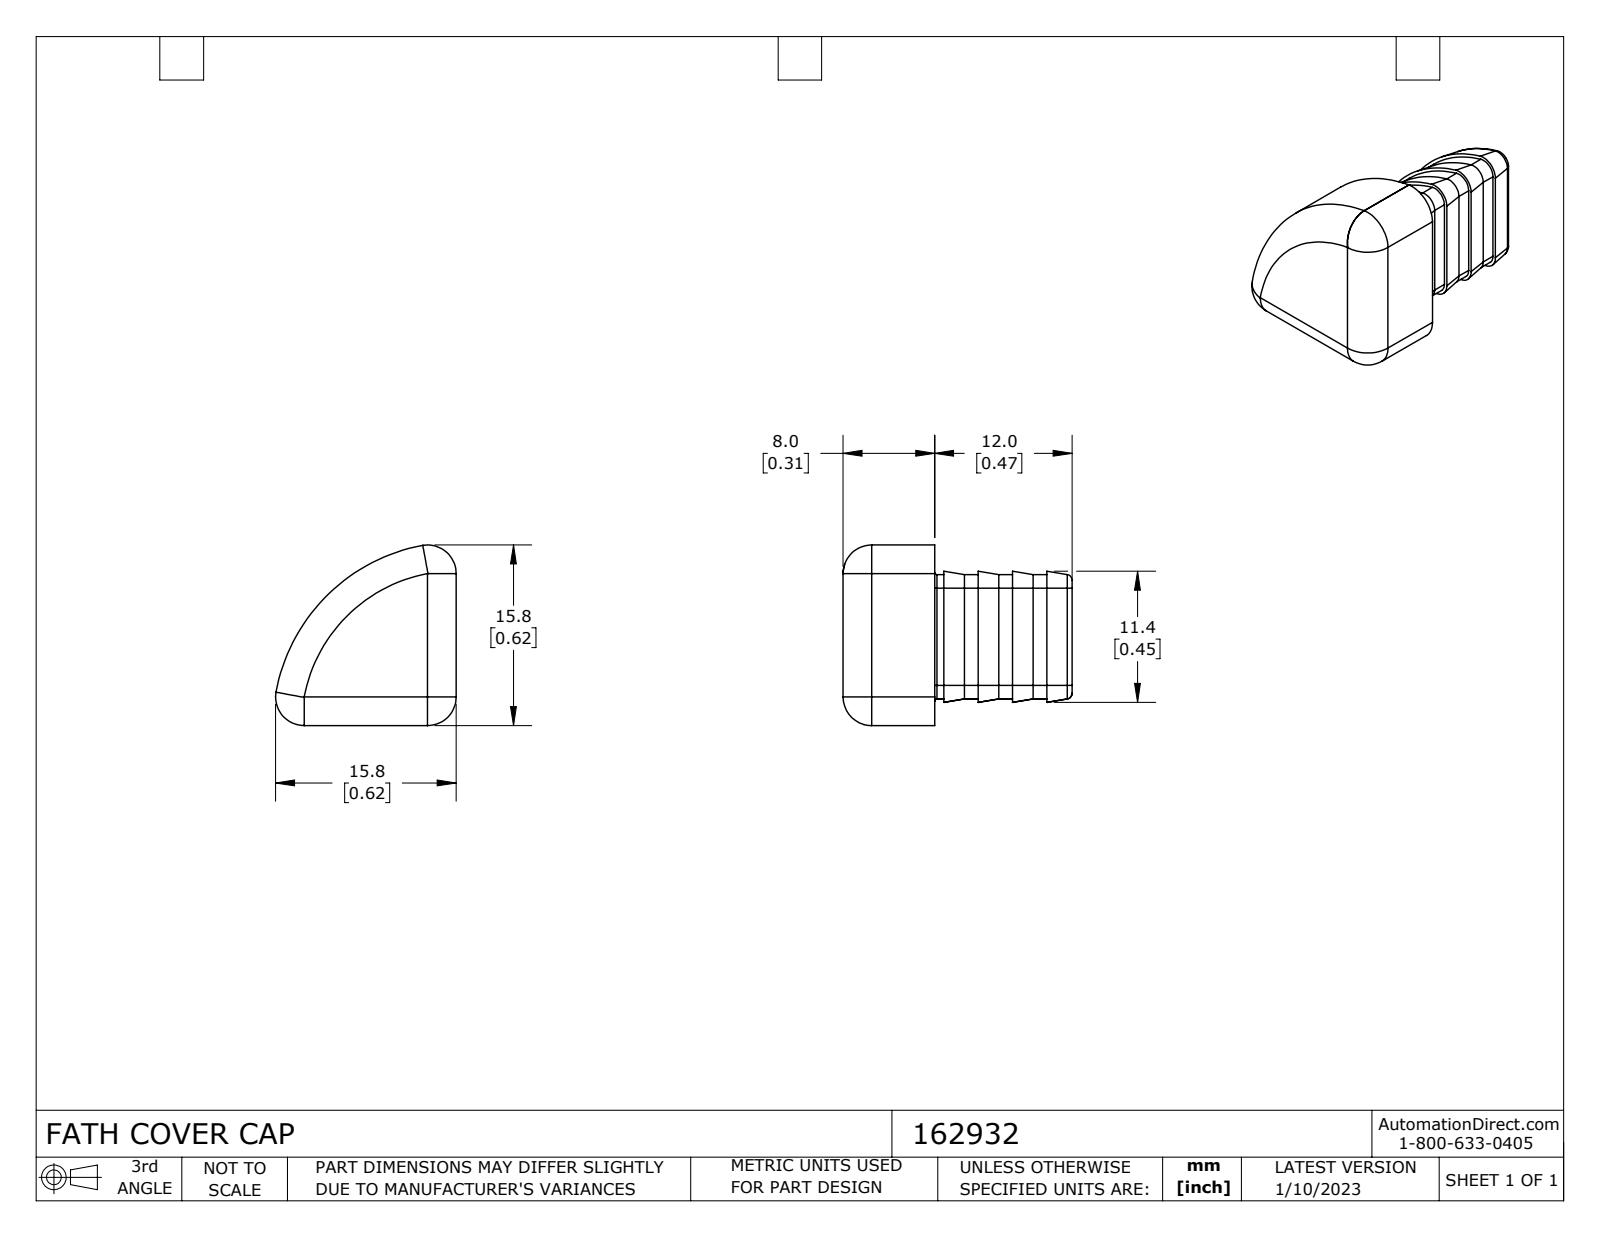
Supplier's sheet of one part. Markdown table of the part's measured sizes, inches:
| quantity | value |
| --- | --- |
| part name | 162932 |
| STEP written by | SolidWorks 2021 (CONFIG_CONTROL_DESIGN) |
| units | inches |
| bodies | 1 solid, 93 faces (30 planar, 31 cylindrical, 32 other) |
| overall size | 0.787 × 0.62 × 0.62 |
| volume | 0.148 in³ |
| surface area | 2.194 in² |
| round holes (diameter × count) | 0.118 × 2 |
| partial cylindrical surfaces (radius × count) | 0.098 × 5, 0.046 × 3, 0.008 × 2, 0.02 × 2, 0.538 × 1, 0.63 × 1 |
| main face-to-face distances | 0.315, 0.019, 0.092, 0.039, 0.472, 0.118, 0.787, 0.236, 0.058, 0.465 |
| hole center spacings | 0.335 |
